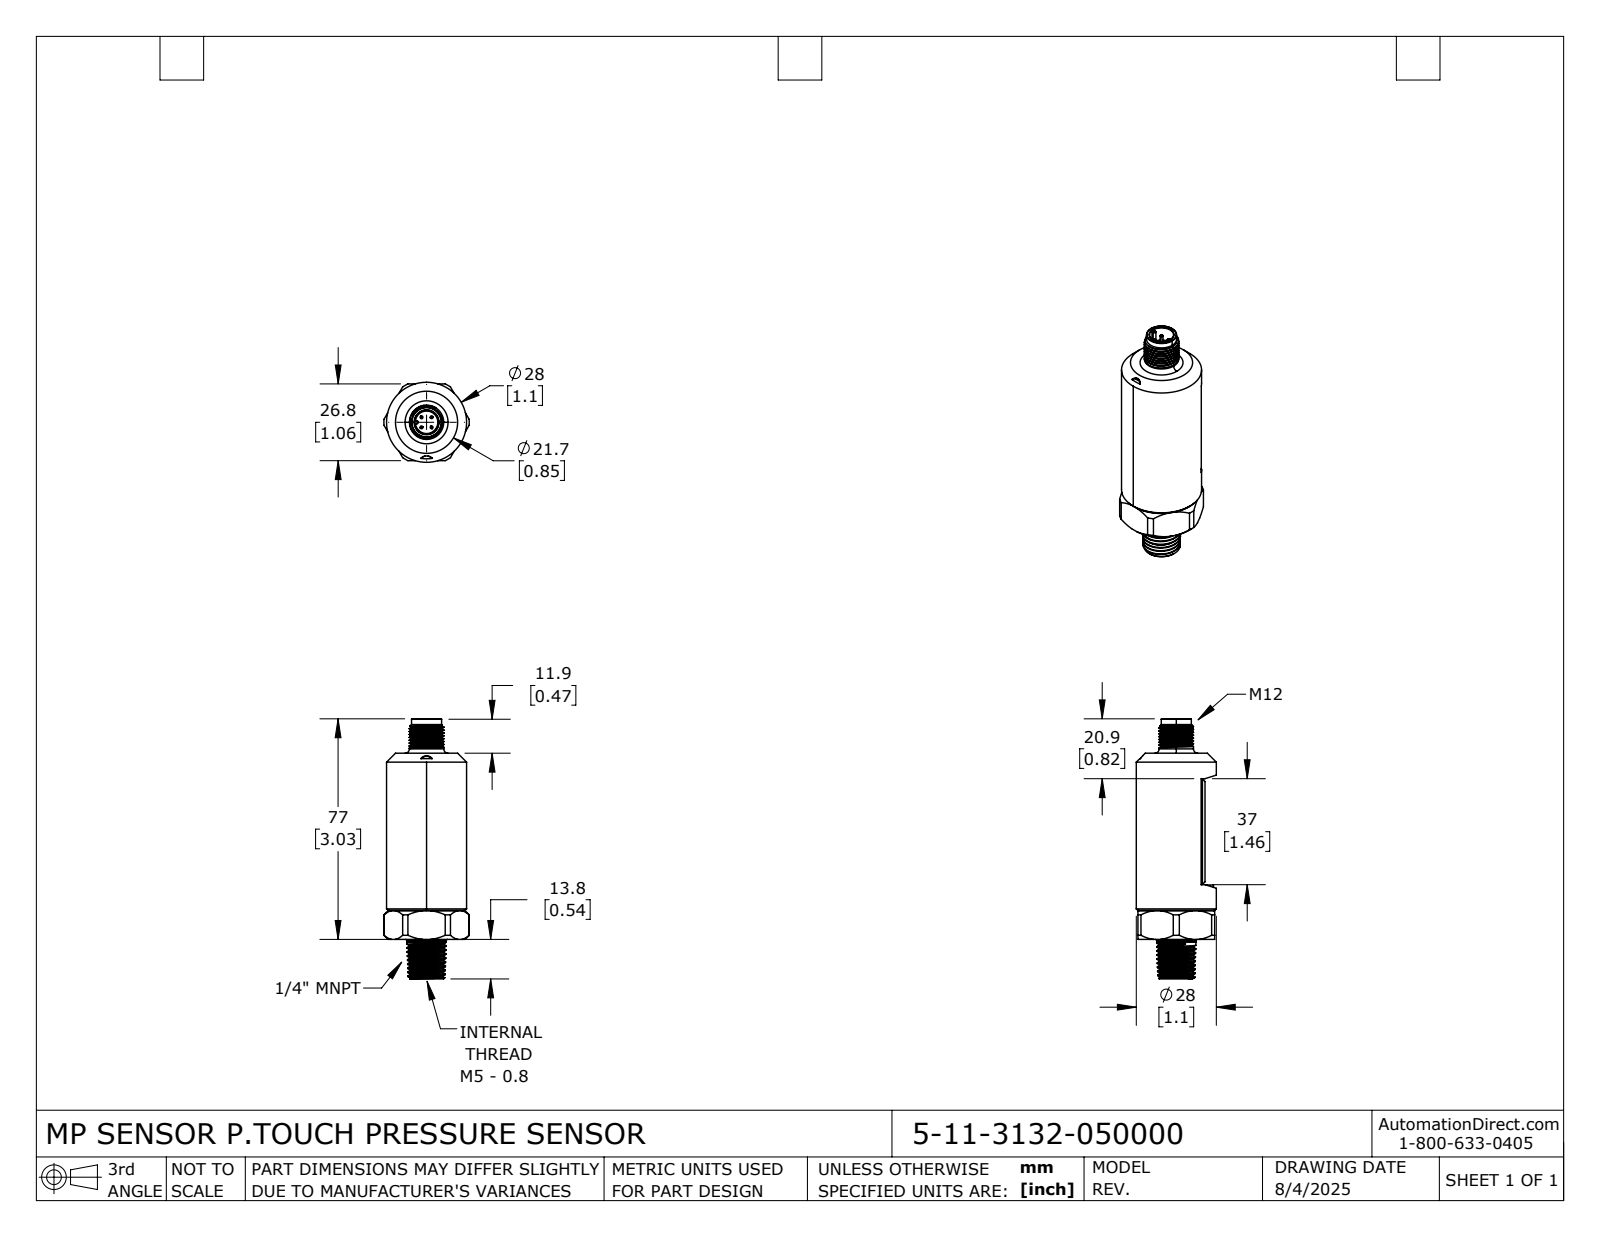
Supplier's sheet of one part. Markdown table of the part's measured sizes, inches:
| quantity | value |
| --- | --- |
| part name | 5-11-3132-050000 |
| STEP written by | SolidWorks 2024 (AUTOMOTIVE_DESIGN) |
| units | inches |
| bodies | 1 solid, 199 faces (46 planar, 68 cylindrical, 85 other) |
| overall size | 3.575 × 1.173 × 1.1 |
| volume | 2.423 in³ |
| surface area | 13.82 in² |
| round holes (diameter × count) | 0.079 × 1, 0.165 × 1, 0.331 × 1 |
| round bosses / shafts (diameter × count) | 0.039 × 4, 1.1 × 1, 1.024 × 1, 0.539 × 1, 0.472 × 1, 0.413 × 1 |
| partial cylindrical surfaces (radius × count) | 0.006 × 2, 0.092 × 1, 0.587 × 1 |
| main face-to-face distances | 1.055, 2.559, 0.922, 0.133, 0.543, 3.102, 0.354, 1.811, 0.35, 0.186 |
